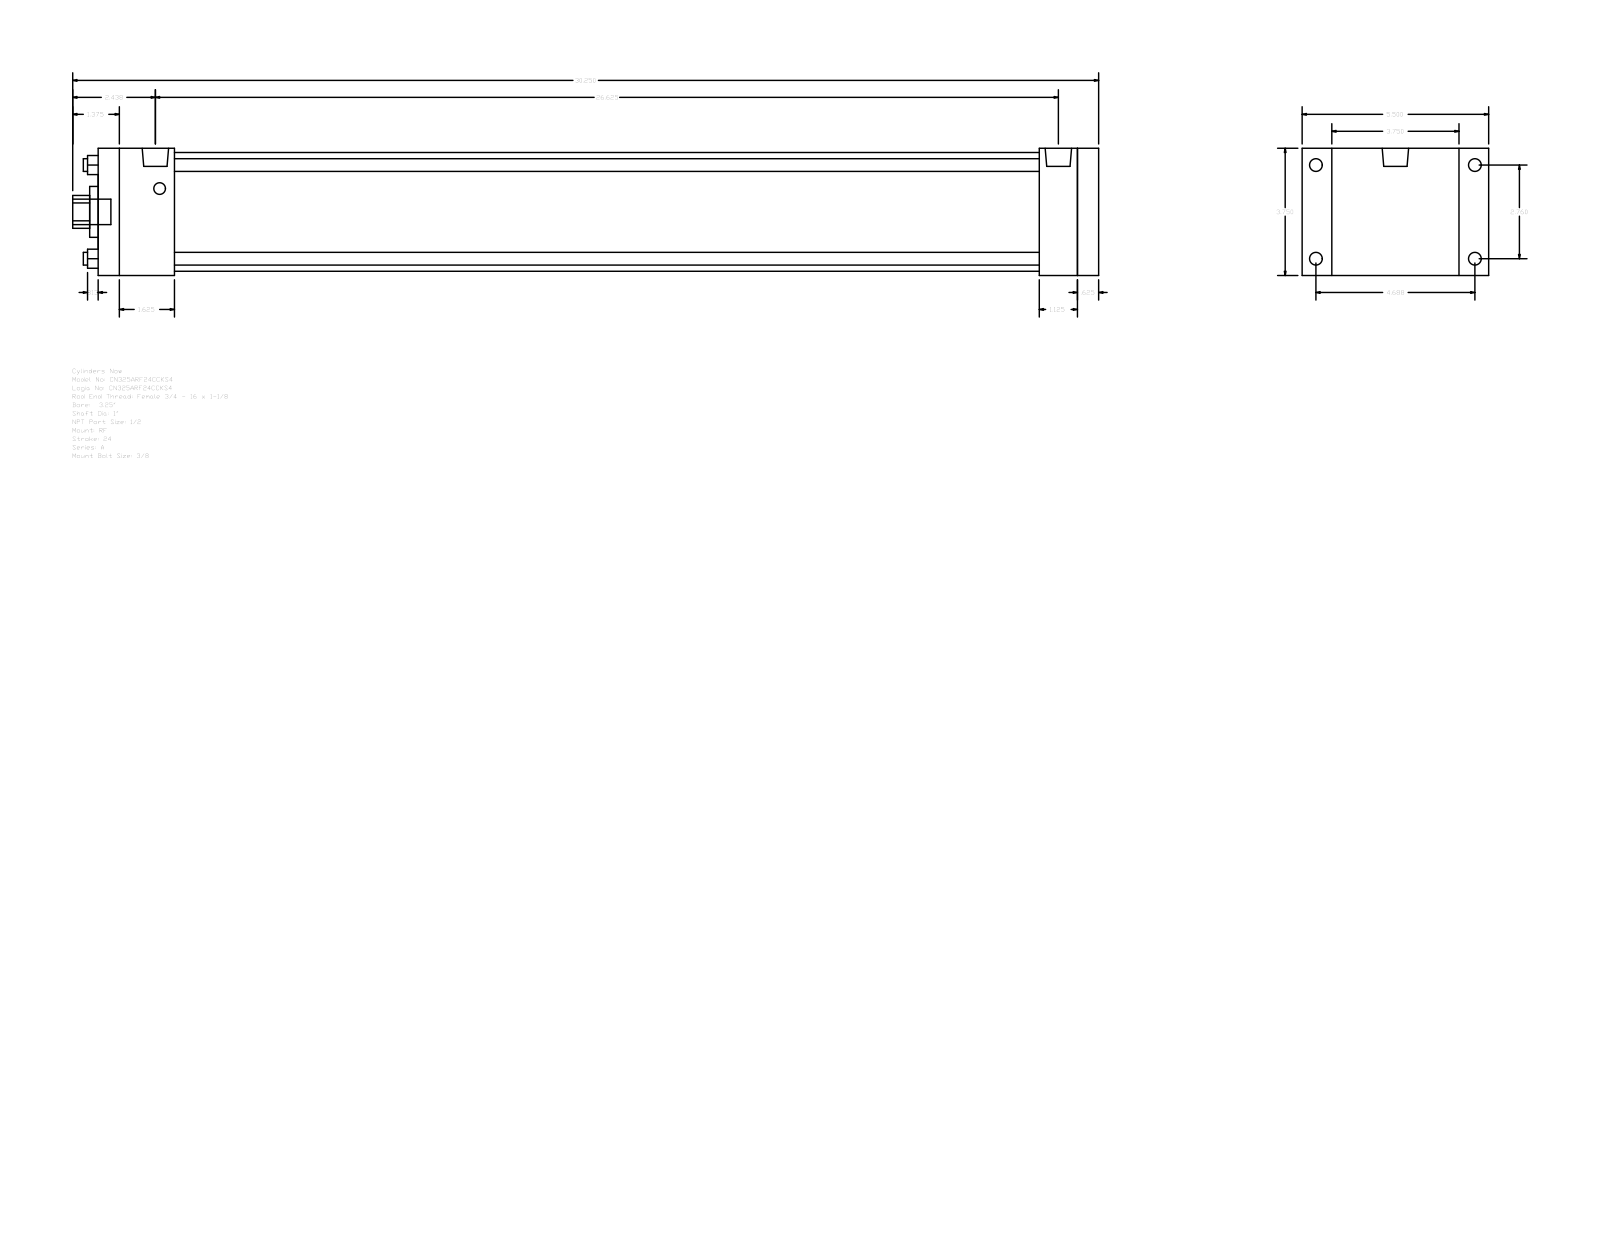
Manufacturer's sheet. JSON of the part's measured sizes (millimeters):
{"part_name": "A_RF__0325_1", "step_written_by": "GSSL Pune (CONFIG_CONTROL_DESIGN)", "units": "millimeters", "bodies": {"solids": 0, "faces": 92, "planar": 64, "cylindrical": 28, "other": 0}, "overall_size": [768.35, 139.7, 95.25], "round_holes": [[9.53, 4], [25.4, 1], [38.1, 1], [88.9, 1]], "round_bosses_or_shafts": [[9.53, 4], [8.73, 4], [19.77, 2], [19.05, 1]], "partial_cylinders_radius": [[12.29, 1]], "face_to_face_distances": [95.24, 749.3, 15.87, 733.43, 22.23, 117.47, 704.85, 28.58, 44.45, 57.15], "hole_center_spacings": [49.57, 70.1, 99.14]}
